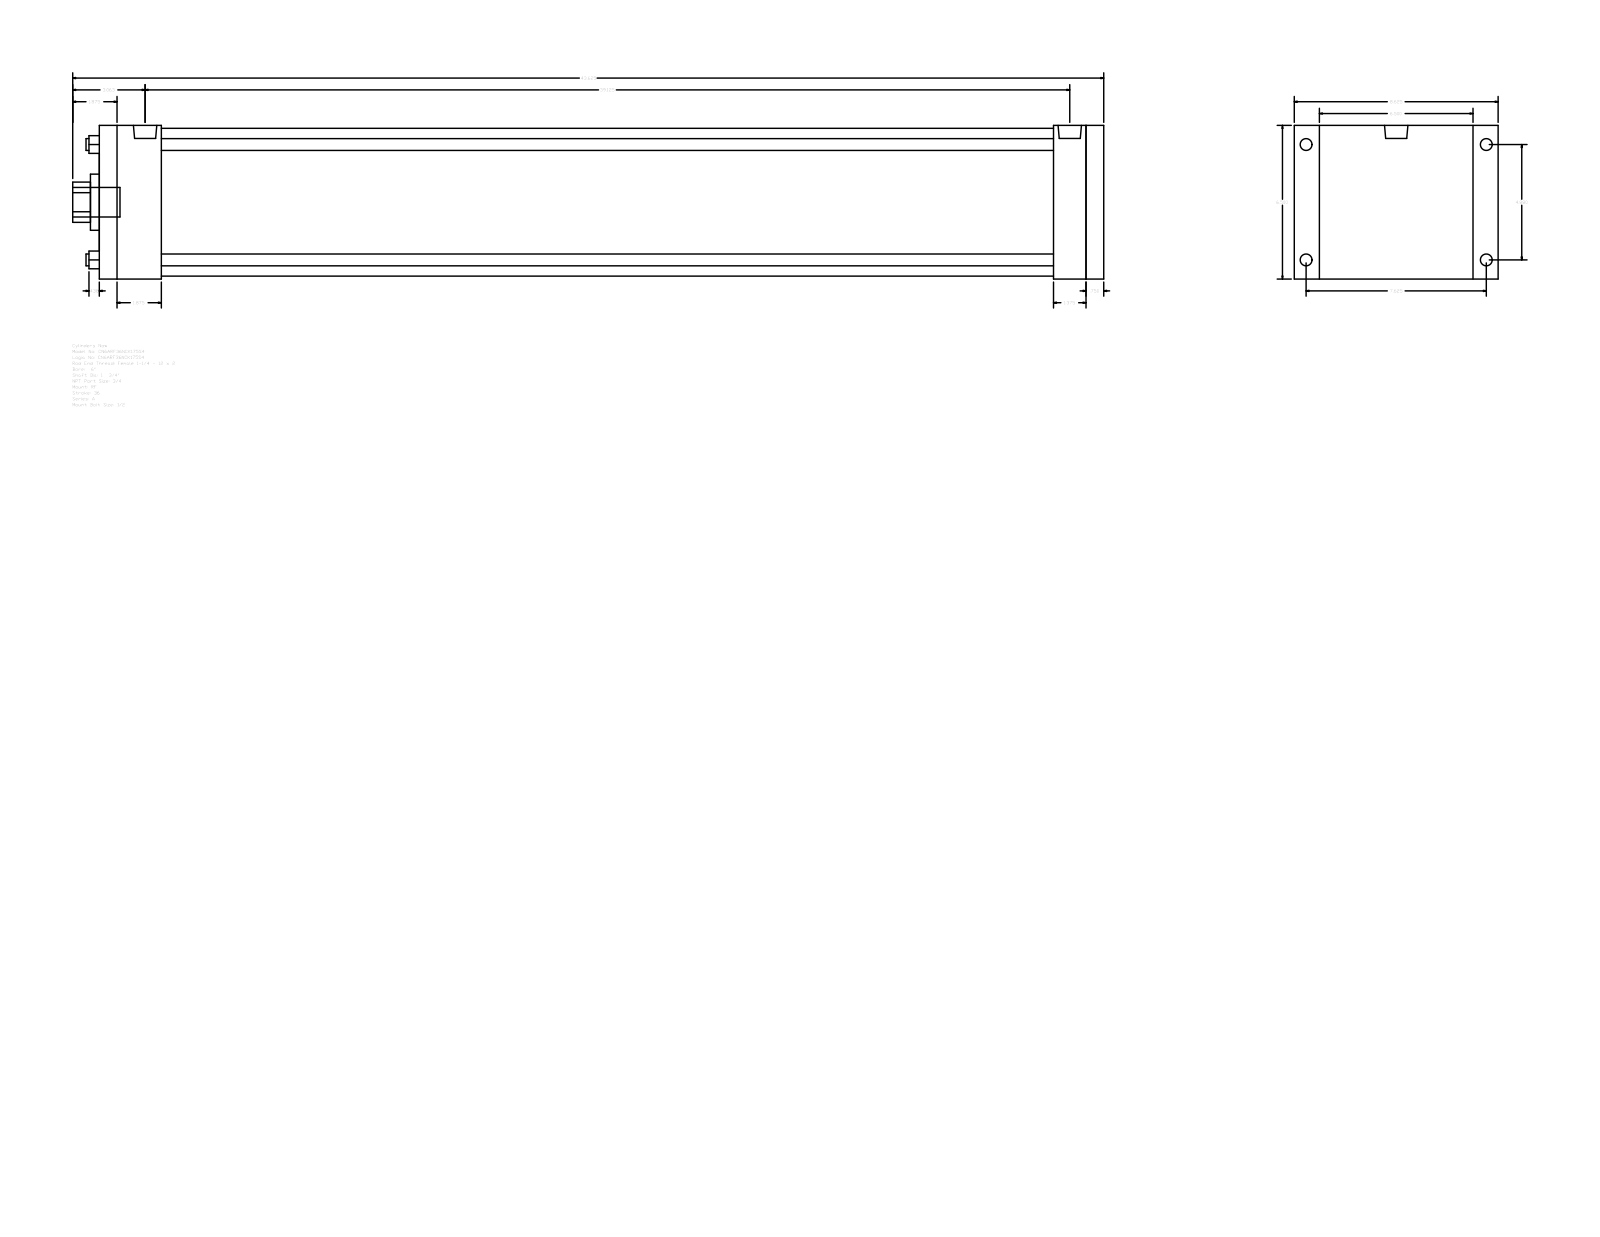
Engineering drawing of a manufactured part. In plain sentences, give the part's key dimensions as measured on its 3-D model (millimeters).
The part is named "A_RF__0600_1.75". Its 3-D file was written by "GSSL Pune (CONFIG_CONTROL_DESIGN)". It is 0 solids with 92 faces: 64 planar, 28 cylindrical and 0 other. Overall it measures 1108.08 by 219.07 by 165.1 millimeters. Round holes: 4 of diameter 12.7, 1 of diameter 44.45, 1 of diameter 60.33, 1 of diameter 158.75. Round bosses or shafts: 4 of diameter 15.08, 4 of diameter 12.7, 2 of diameter 25.12, 1 of diameter 31.75. Partial cylindrical surfaces (rounded edges, fillets, slot ends): 1 of radius 21.63. The main face-to-face distances are 165.1, 1079.51, 19.05, 1060.46, 66.68, 993.78, 1012.83, 1025.53, 958.85, 34.93. The hole center spacings are 87.65, 123.96, 175.31.
